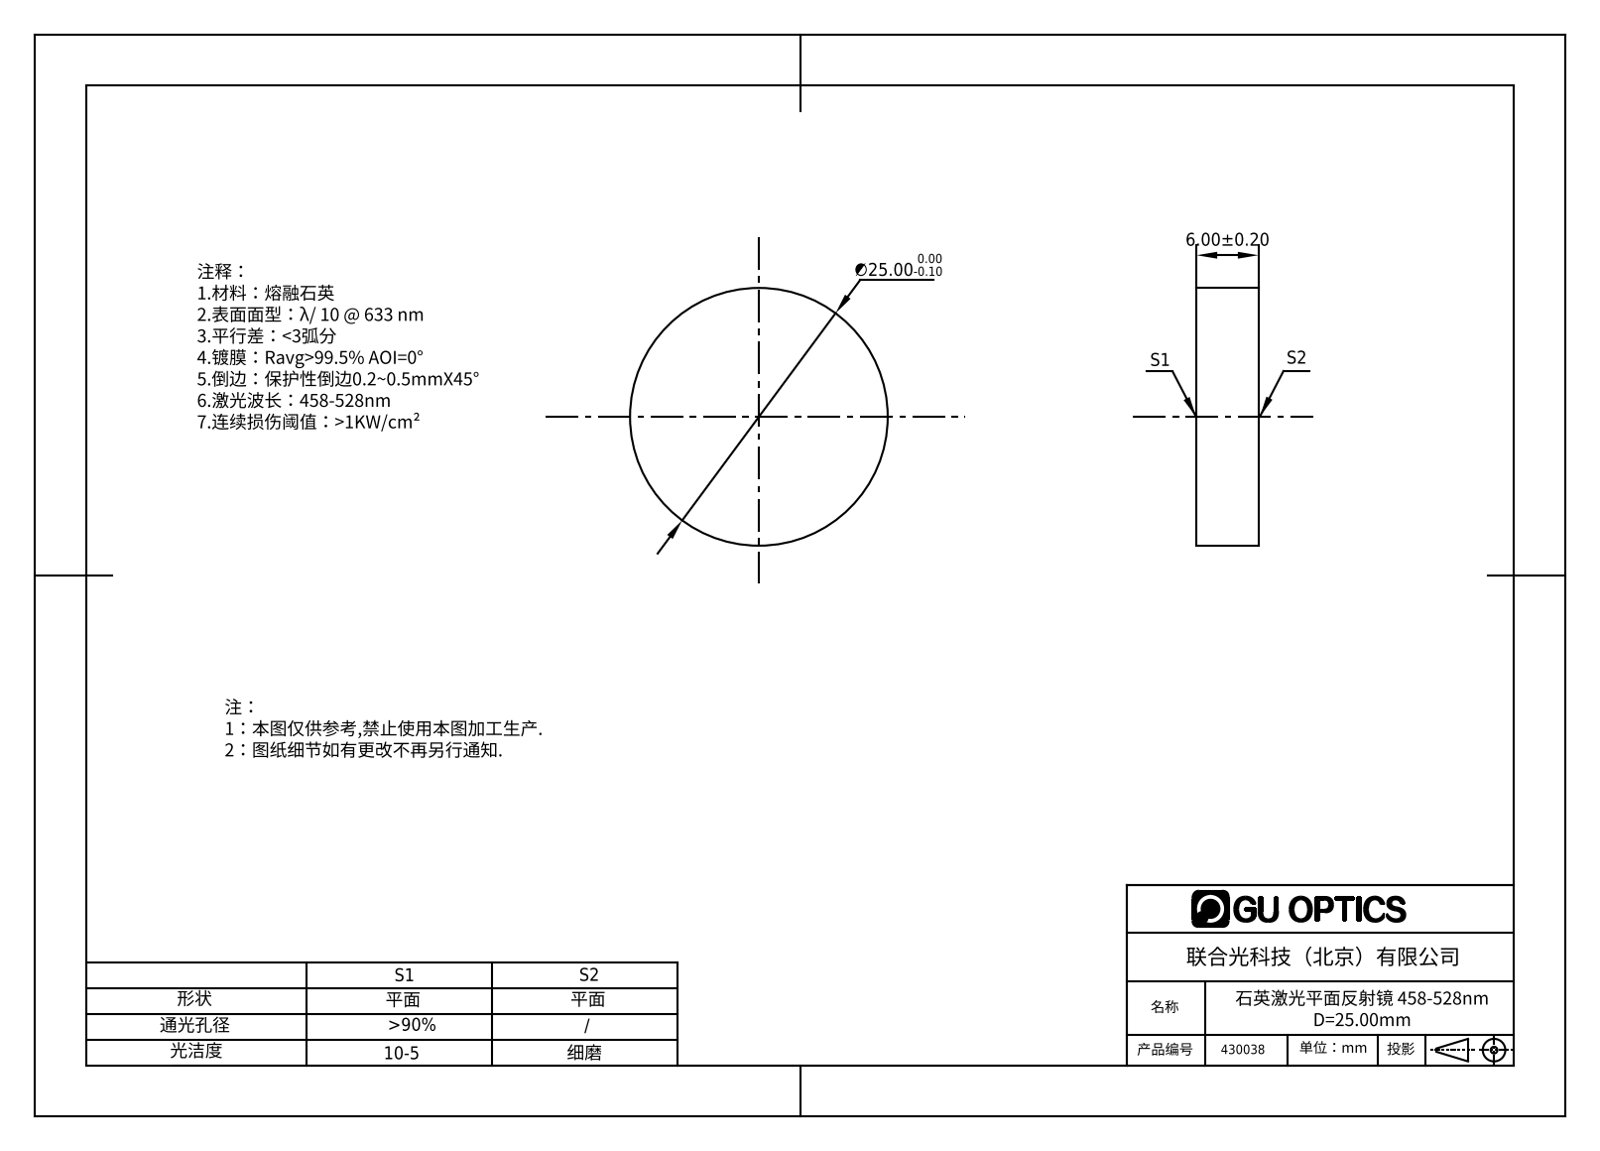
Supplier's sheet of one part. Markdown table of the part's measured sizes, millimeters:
| quantity | value |
| --- | --- |
| part name | 430008 |
| STEP written by | SolidWorks 2016 (AUTOMOTIVE_DESIGN) |
| units | millimeters |
| bodies | 1 solid, 4 faces (2 planar, 2 cylindrical, 0 other) |
| overall size | 25 × 25 × 6 |
| volume | 2 945 mm³ |
| surface area | 1 453 mm² |
| round bosses / shafts (diameter × count) | 25 × 1 |
| main face-to-face distances | 6 |
